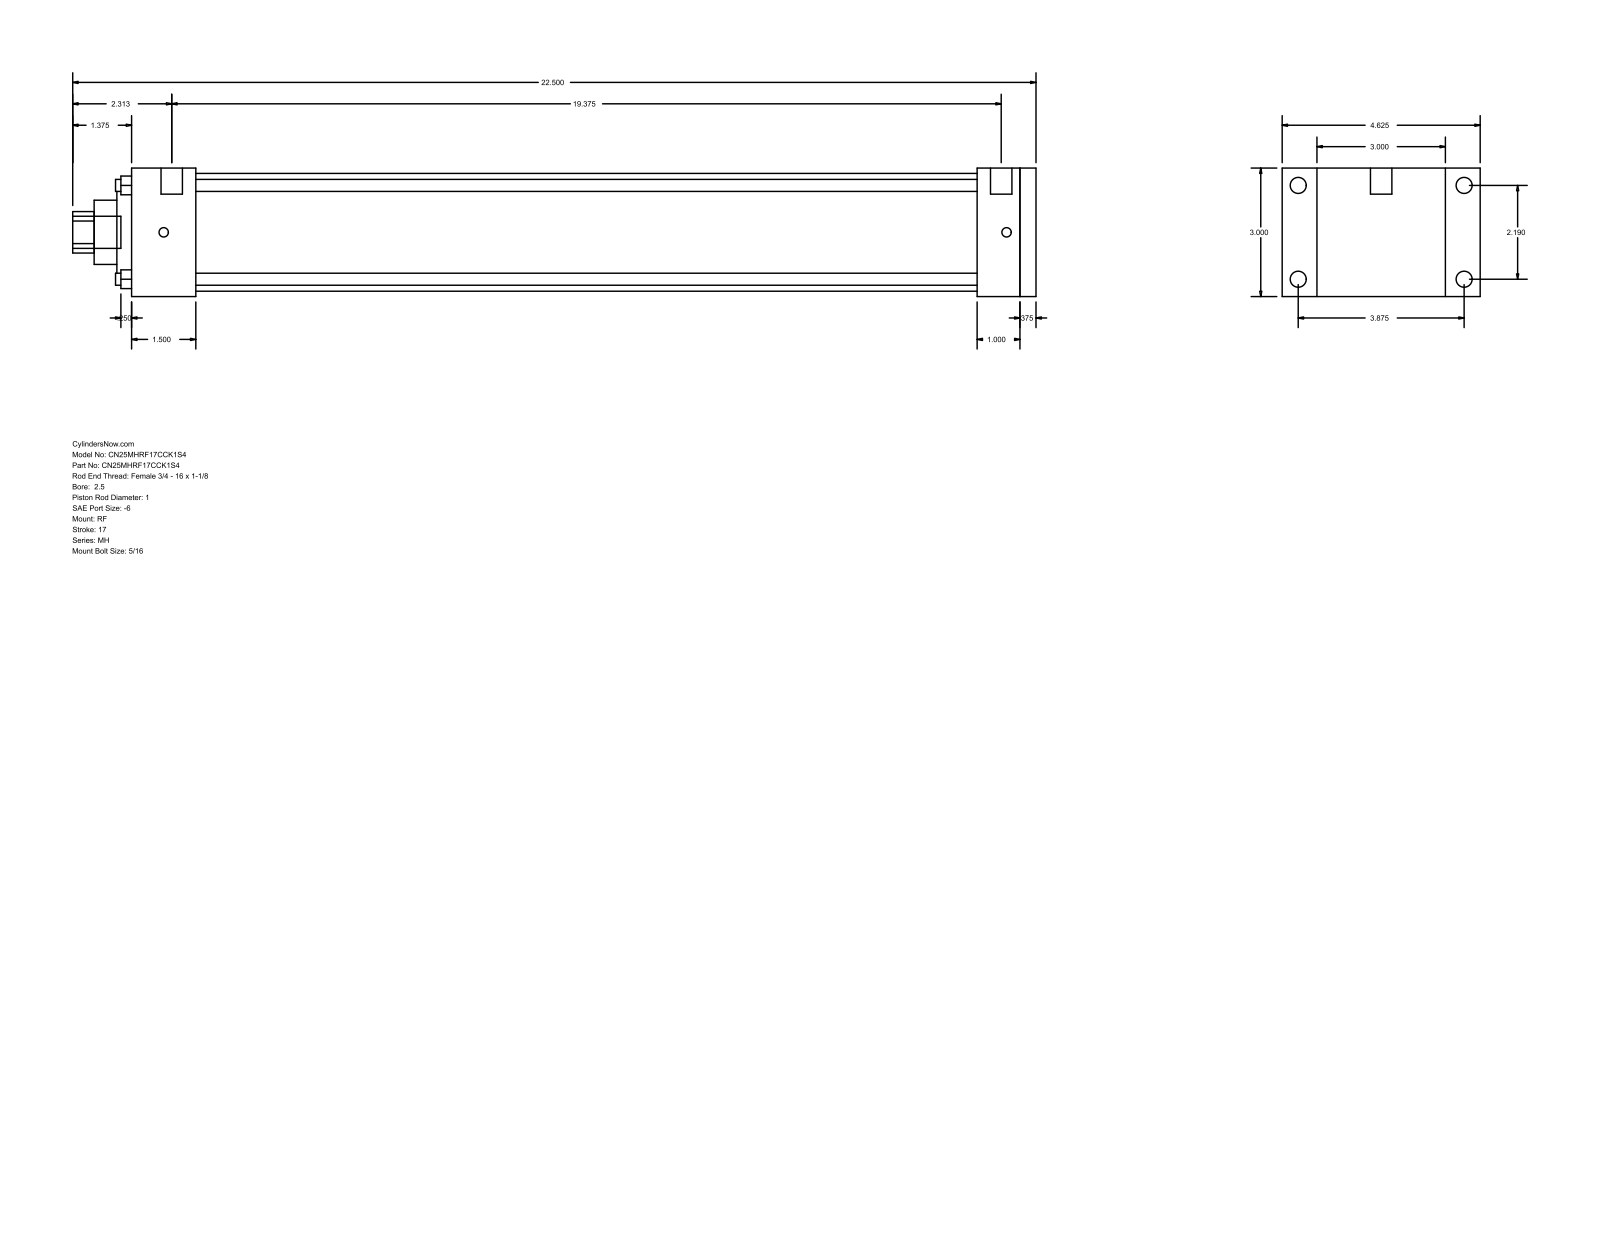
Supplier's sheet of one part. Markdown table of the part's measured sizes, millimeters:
| quantity | value |
| --- | --- |
| part name | MH_RF__0250_1 |
| STEP written by | GSSL Pune (CONFIG_CONTROL_DESIGN) |
| units | millimeters |
| bodies | 0 solids, 94 faces (65 planar, 29 cylindrical, 0 other) |
| overall size | 571.5 × 117.47 × 76.2 |
| round holes (diameter × count) | 7.14 × 4, 25.4 × 1, 38.1 × 1, 60.33 × 1, 69.85 × 1 |
| round bosses / shafts (diameter × count) | 9.53 × 4, 5.56 × 4, 12.7 × 2, 19.05 × 1 |
| partial cylindrical surfaces (radius × count) | 12.29 × 1 |
| main face-to-face distances | 76.2, 9.52, 536.58, 527.06, 25.4, 34.92, 501.66, 38.11, 463.55, 488.95 |
| hole center spacings | 39.33, 55.62, 78.66 |
